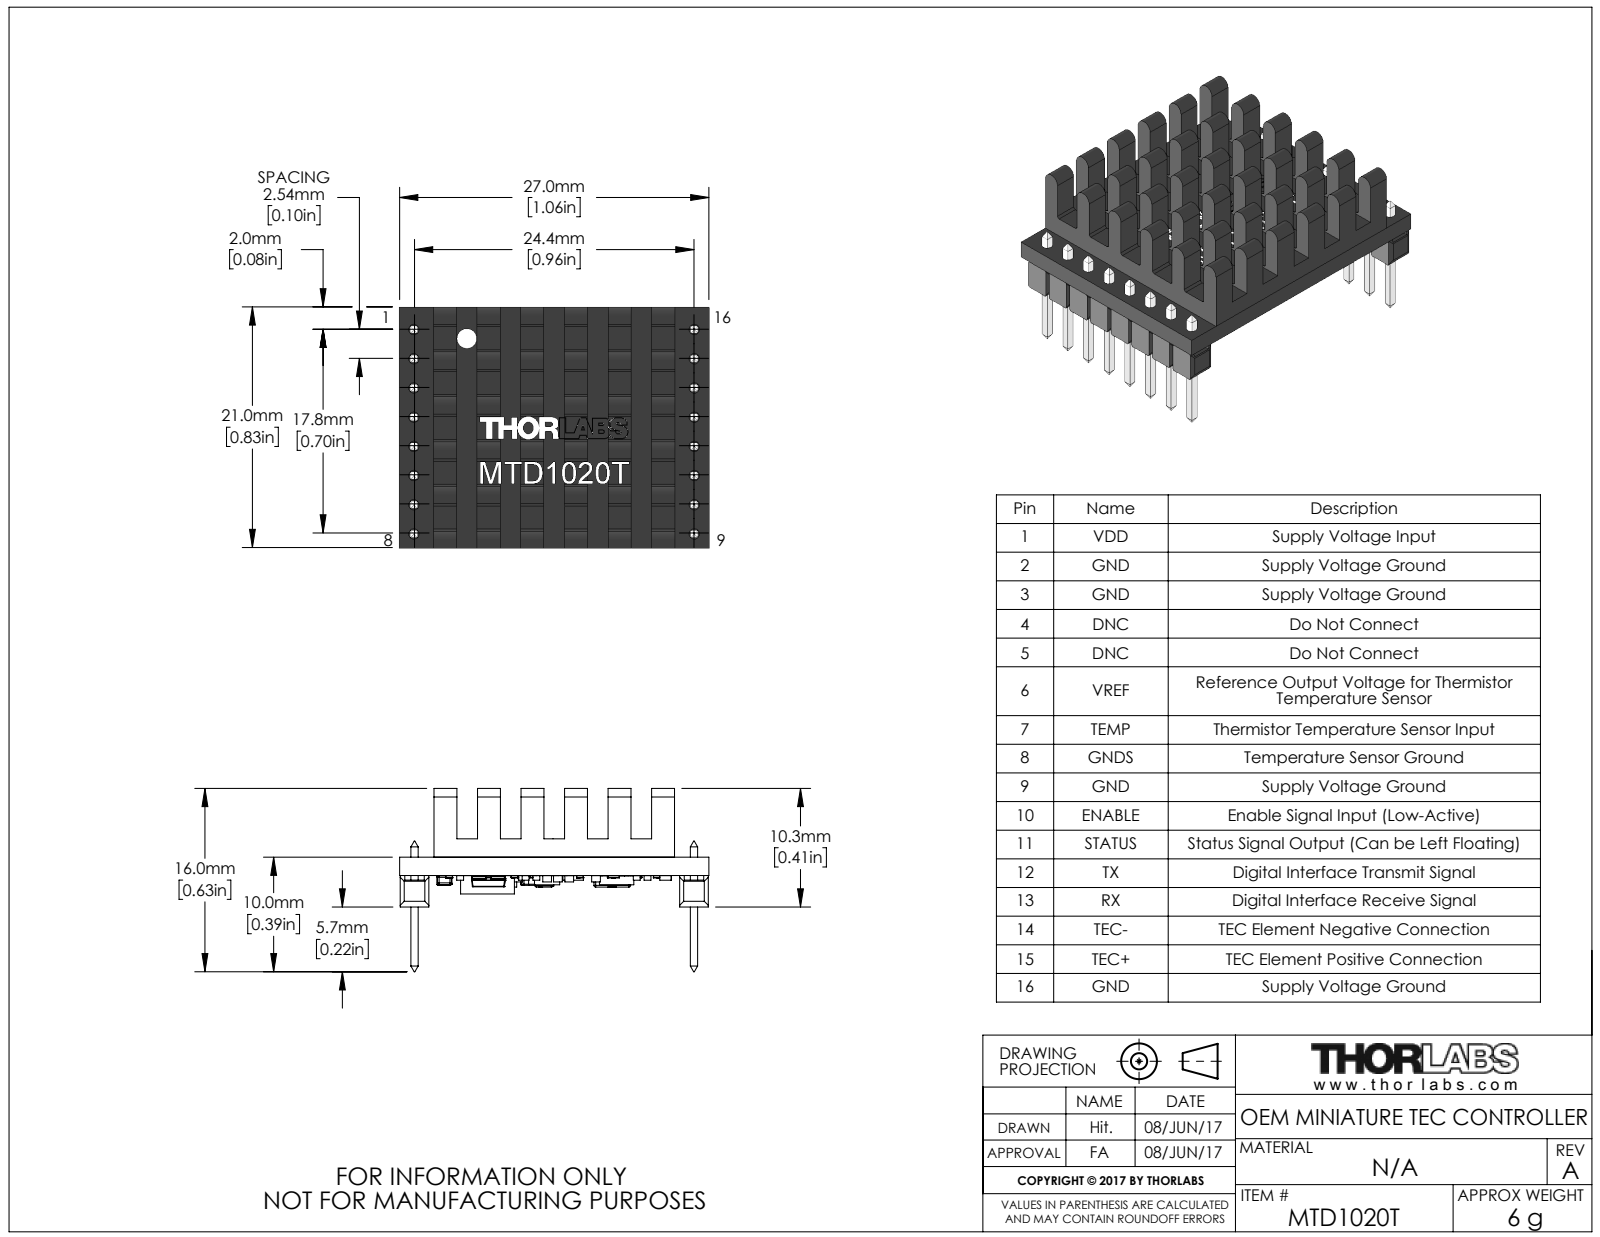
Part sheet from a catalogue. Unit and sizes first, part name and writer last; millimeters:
Units: millimetres
Overall size (bounding box): 27 × 21 × 16
Round holes (diameter × count): ⌀0.91 ×16, ⌀1.7 ×1
Partial cylindrical surfaces — rounded edges, fillets, slot ends (radius × count): R0.15 ×77, R0.1 ×24, R0.2 ×20, R0.75 ×6, R0.19 ×2, R0.14 ×1, R0.15 ×1
Main face-to-face distances: 1.6, 3.8, 3.9, 7.6, 7.8, 1.8, 2, 11.4, 1.5, 11.7
Hole centre spacings: 2.54, 24.53, 5.08, 24.92, 7.62, 25.56, 10.16, 24.4
Bodies: 0 solids, 3255 faces (2029 planar, 472 cylindrical, 754 other)
Part name (STEP PRODUCT): MTN009756-E0W
STEP written by: SolidWorks 2016 (AUTOMOTIVE_DESIGN)
